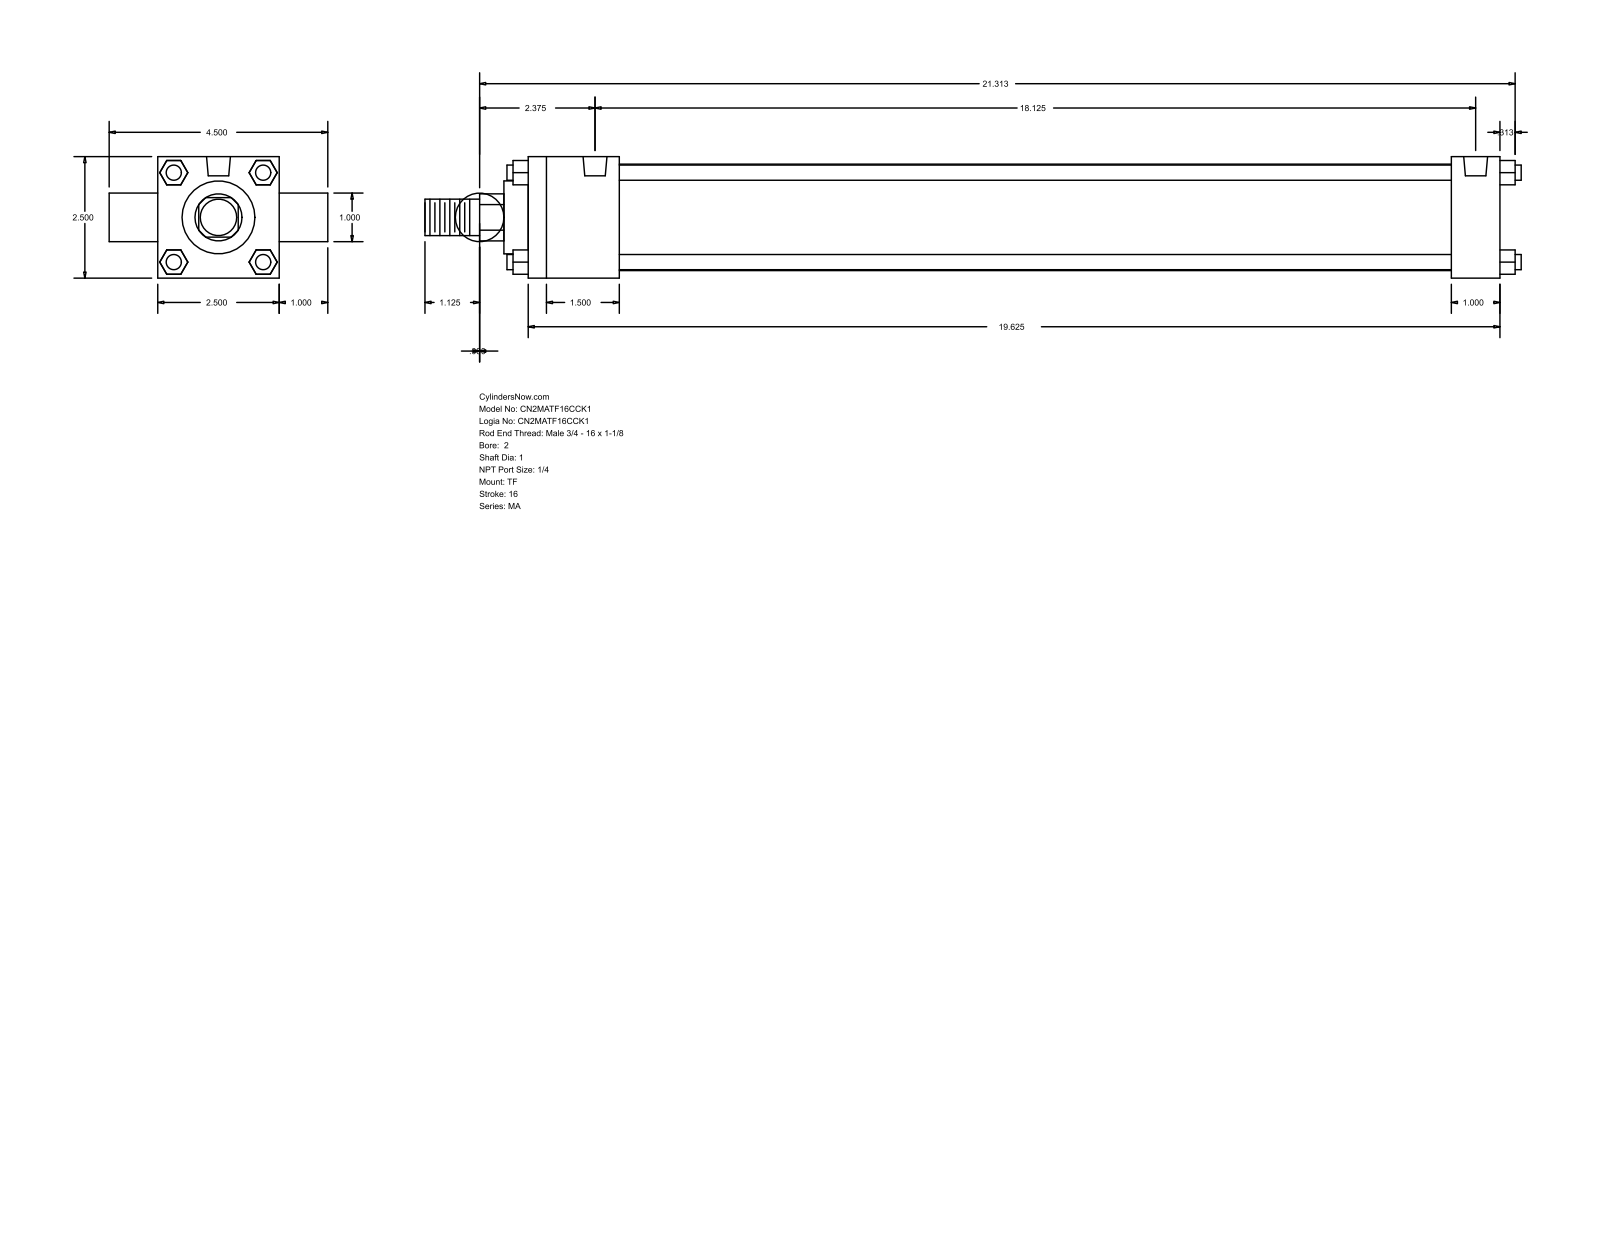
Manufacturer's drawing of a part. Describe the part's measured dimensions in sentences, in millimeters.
The part is named "MA_TF__0200_1". Its 3-D file was written by "GSSL Pune (CONFIG_CONTROL_DESIGN)". It is 0 solids with 120 faces: 92 planar, 28 cylindrical and 0 other. Overall it measures 573.09 by 114.3 by 63.5 millimeters. Round holes: 3 of diameter 7.94, 2 of diameter 12.49. Round bosses or shafts: 4 of diameter 7.94, 2 of diameter 25.4, 1 of diameter 55.63, 1 of diameter 38.1, 1 of diameter 19.05. Partial cylindrical surfaces (rounded edges, fillets, slot ends): 1 of radius 12.29. The main face-to-face distances are 63.5, 25.4, 508, 12.7, 47.63, 482.6, 434.97, 460.37, 88.9, 40.47. The hole center spacings are 460.37.
